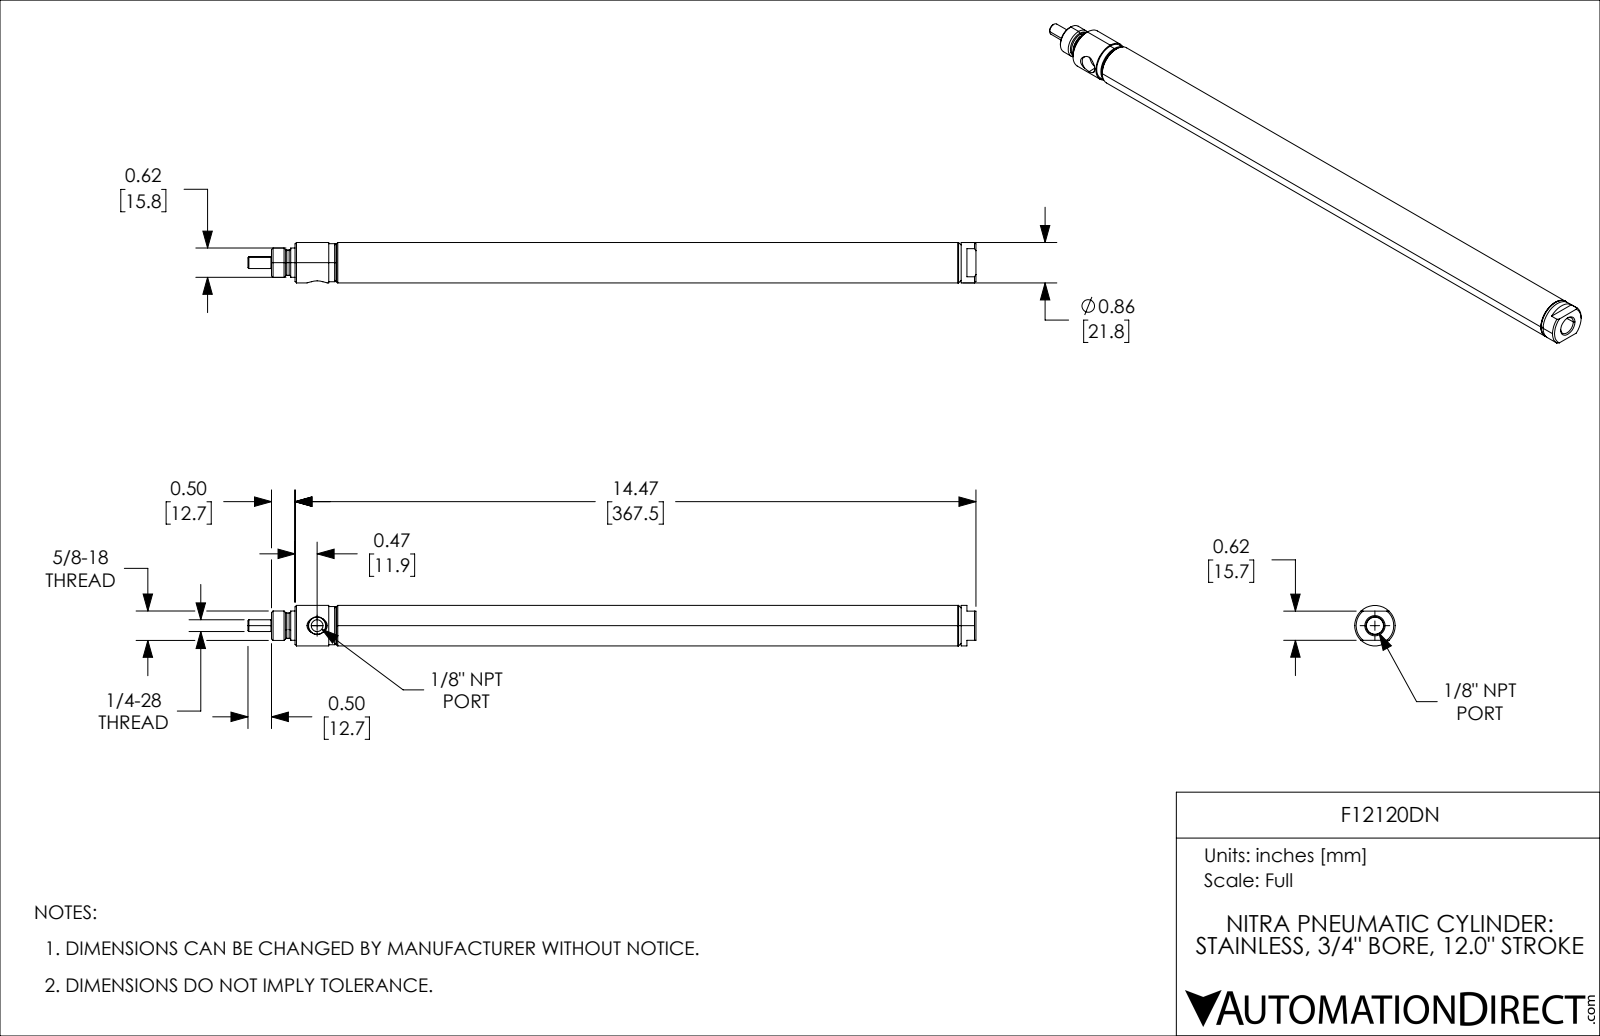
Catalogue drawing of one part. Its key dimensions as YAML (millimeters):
part_name: "F12120DN; F12120DN_3; F12120DN_7; F12120DN_5 (+1 more)"
step_written_by: "SolidWorks 2021 (CONFIG_CONTROL_DESIGN)"
units: millimeters
bodies: {solids: 4, faces: 124, planar: 22, cylindrical: 46, other: 56}
overall_size: [392.91, 21.84, 21.84]
volume: 57736
surface_area: 59454
round_holes:
  - {diameter: 6.35, count: 1}
  - {diameter: 6.95, count: 1}
  - {diameter: 12.7, count: 1}
  - {diameter: 17.83, count: 1}
round_bosses_or_shafts:
  - {diameter: 21.84, count: 1}
  - {diameter: 20.57, count: 1}
  - {diameter: 19.35, count: 1}
  - {diameter: 15.88, count: 1}
  - {diameter: 15.81, count: 1}
  - {diameter: 13.68, count: 1}
  - {diameter: 6.35, count: 1}
  - {diameter: 5.84, count: 1}
face_to_face_distances: [21.43, 304.8, 326.23, 339.72, 34.92, 13.49, 12.7, 27.79, 332.59, 354.02]
